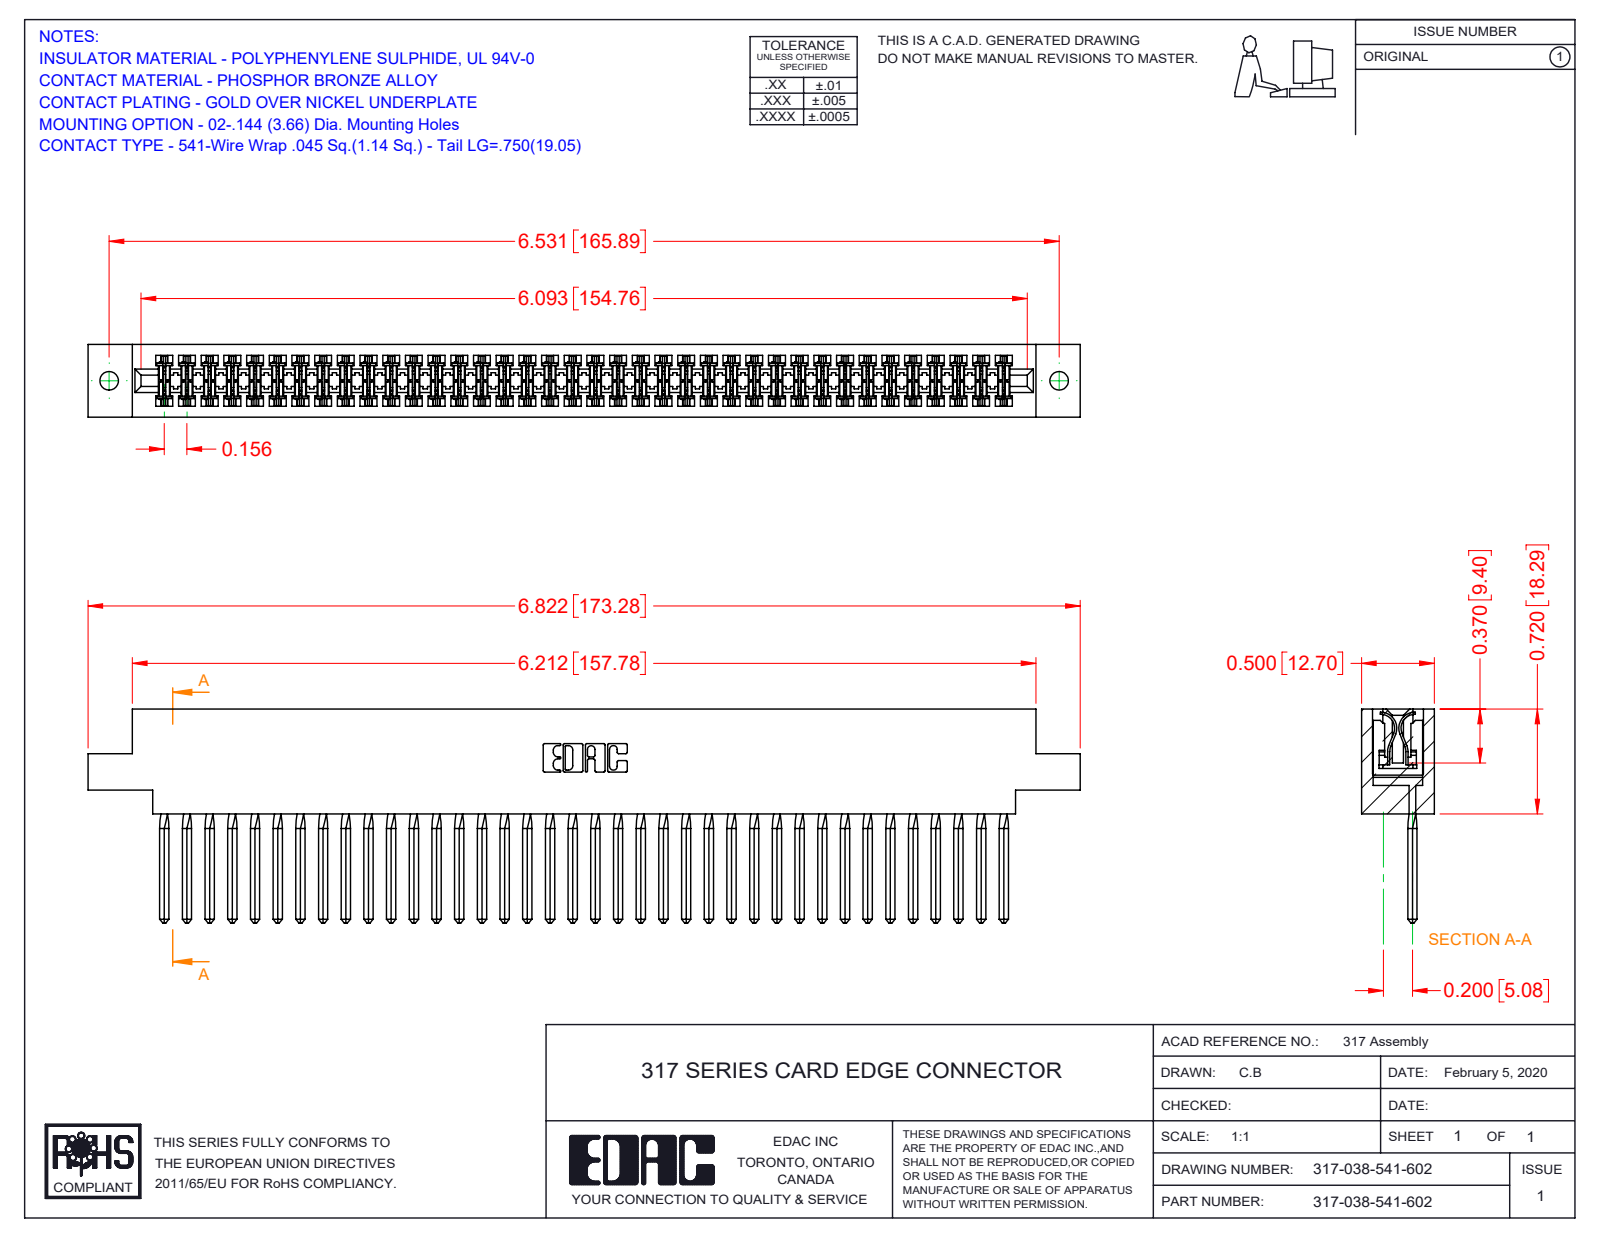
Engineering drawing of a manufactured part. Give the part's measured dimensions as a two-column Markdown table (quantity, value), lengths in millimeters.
| quantity | value |
| --- | --- |
| part name | 317-038-541-602; 317 Part_.144 Dia; 317-290-002_541 |
| STEP written by | SolidWorks 2016 (CONFIG_CONTROL_DESIGN) |
| units | millimeters |
| bodies | 39 solids, 5878 faces (4770 planar, 956 cylindrical, 152 other) |
| overall size | 173.3 × 37.3 × 12.7 |
| volume | 27 940 mm³ |
| surface area | 39 080 mm² |
| round holes (diameter × count) | 3.3 × 2 |
| partial cylindrical surfaces (radius × count) | 0.4 × 76, 0.3 × 22, 0.2 × 6, 0.8 × 6, 0.7 × 3, 2.4 × 2, 2.5 × 2, 2.8 × 2 |
| main face-to-face distances | 12.7, 1.9, 10.8, 8.9, 5, 2.8, 18.3, 2.9, 5.4, 7.3 |
| hole center spacings | 165.9 |
